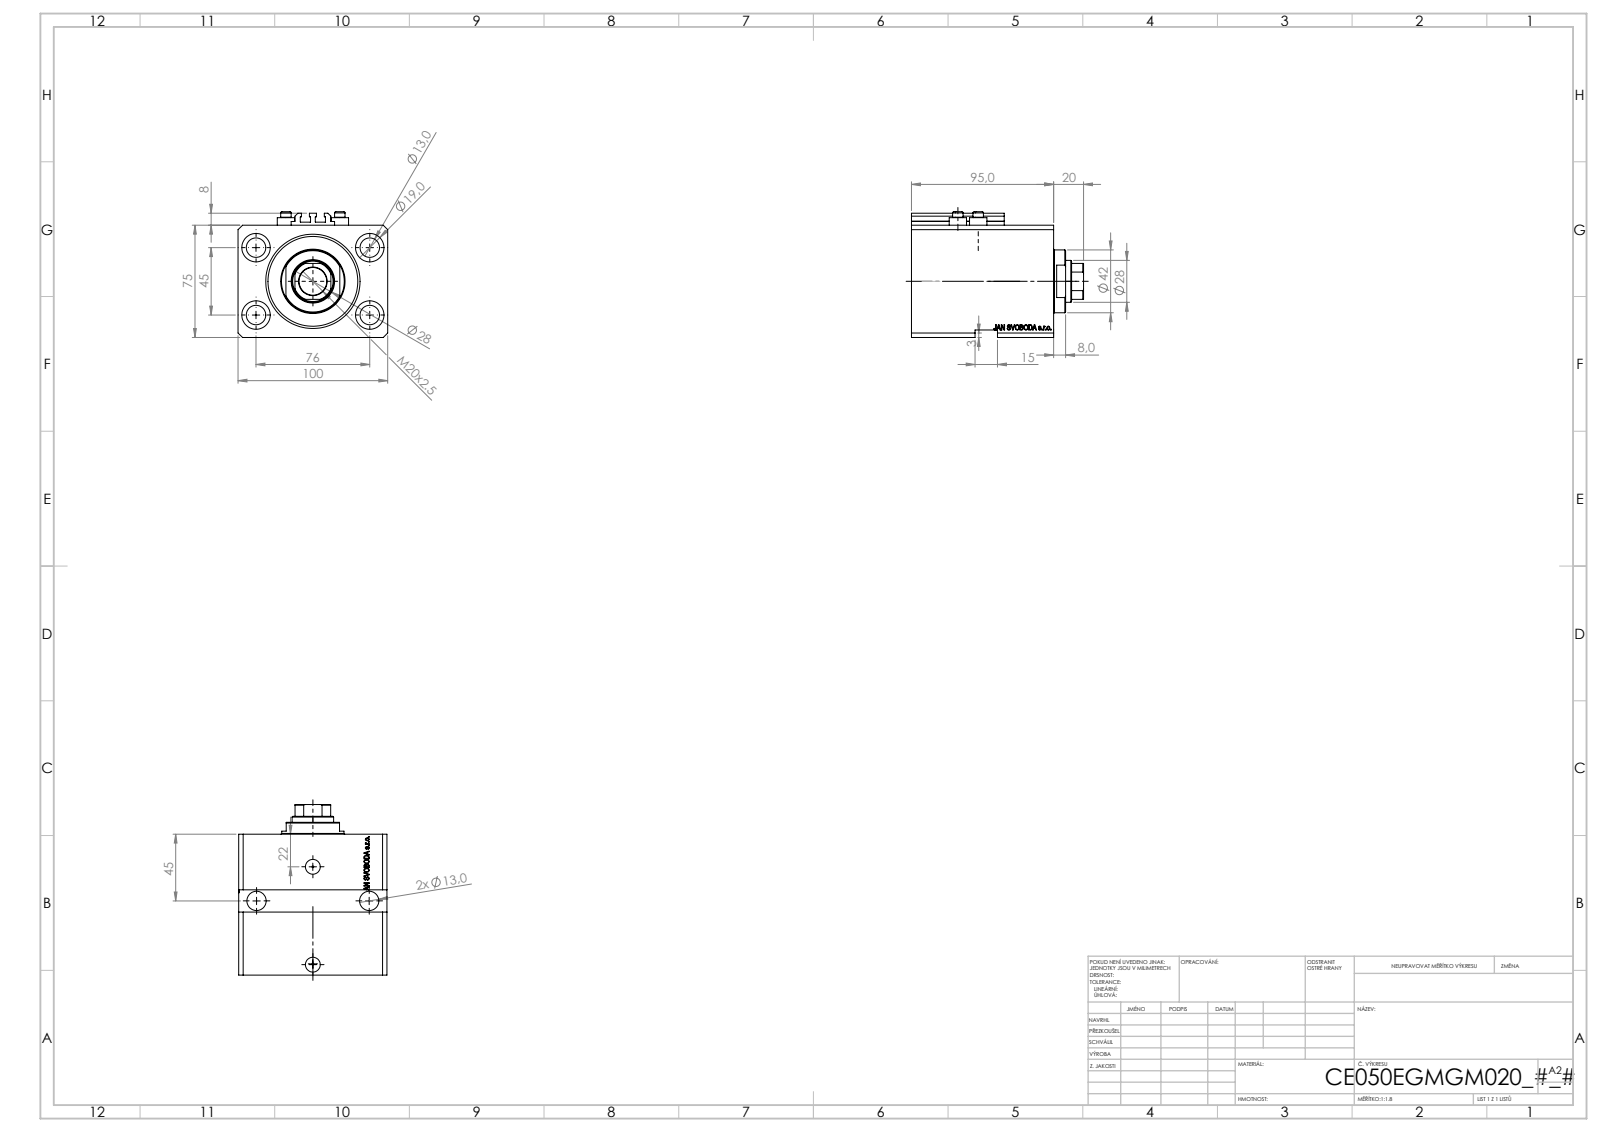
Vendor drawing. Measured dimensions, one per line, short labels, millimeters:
name: V250CE_E_Body; V250CE_C_VCP; V250CE_VC_E; ALLEN BOLT V250CE
written by: SolidWorks 2019 (CONFIG_CONTROL_DESIGN)
unit: mm
bodies: 8 solids, 1088 faces (535 planar, 126 cylindrical, 427 other)
size: 114.9 × 100 × 84
volume: 610 933 mm³; area: 123 534 mm²
holes: 6× ⌀13, 4× ⌀1.25, 4× ⌀4, 4× ⌀19, 2× ⌀10, 2× ⌀13.16, 2× ⌀20, 1× ⌀18.5, 1× ⌀28, 1× ⌀50, 1× ⌀63
bosses: 4× ⌀11.6, 4× ⌀7, 1× ⌀42
rounds: 10× R0.2, 1× R13.5
face distances: 75, 100, 95, 11.9, 83.1, 68.4, 56.5, 26.6, 5, 48.4
hole spacings: 44.16, 76, 13.6, 20.72, 27.59, 29.58, 30, 33.62
